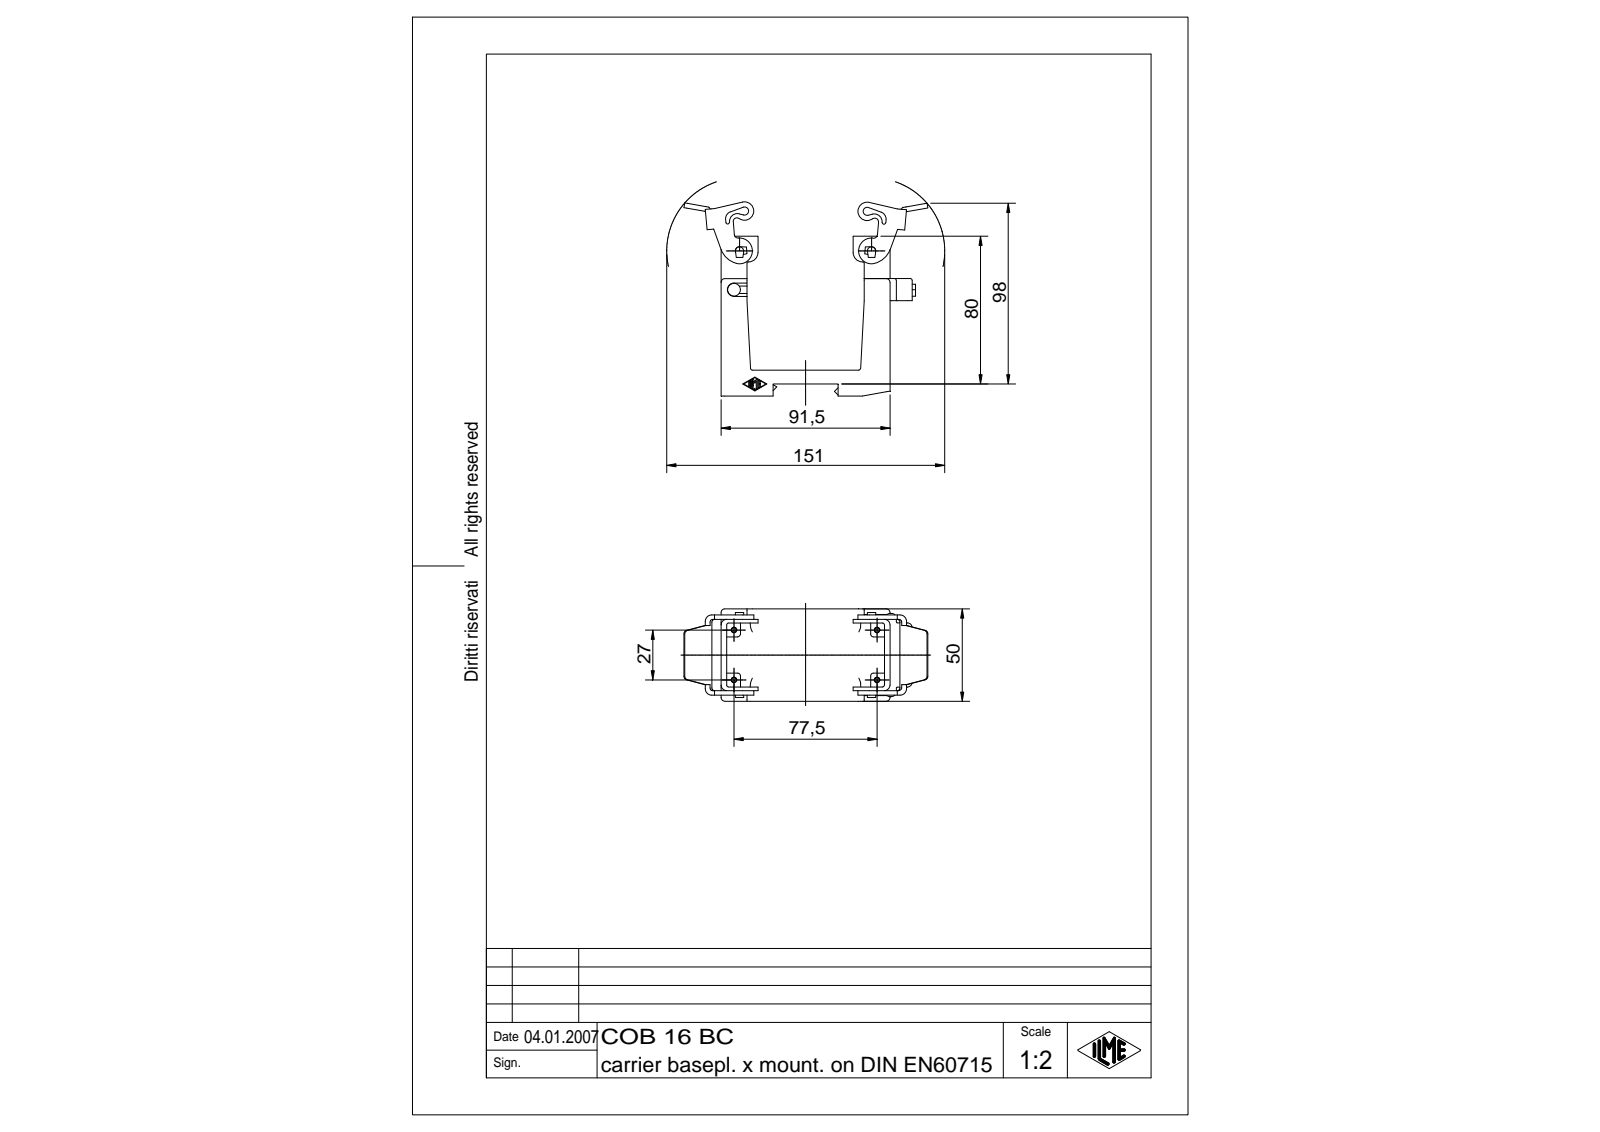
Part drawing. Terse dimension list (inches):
name: Einsatzhalter für die Montage auf DIN Schiene
written by: Autodesk Inventor 7 (AUTOMOTIVE_DESIGN)
unit: in
bodies: 1 solid, 522 faces (224 planar, 183 cylindrical, 115 other)
size: 5.201 × 4.137 × 1.969
volume: 5.994 in³; area: 62.53 in²
bosses: 1× ⌀0.276, 1× ⌀0.177, 1× ⌀0.157
rounds: 18× R0.039, 18× R0.079, 14× R0.01, 8× R0.059, 5× R0.197, 4× R0.02, 4× R0.098, 4× R0.118
face distances: 0.295, 0.551, 1.969, 0.256, 0.079, 0.118, 3.484, 0.303, 1.665, 3.602
